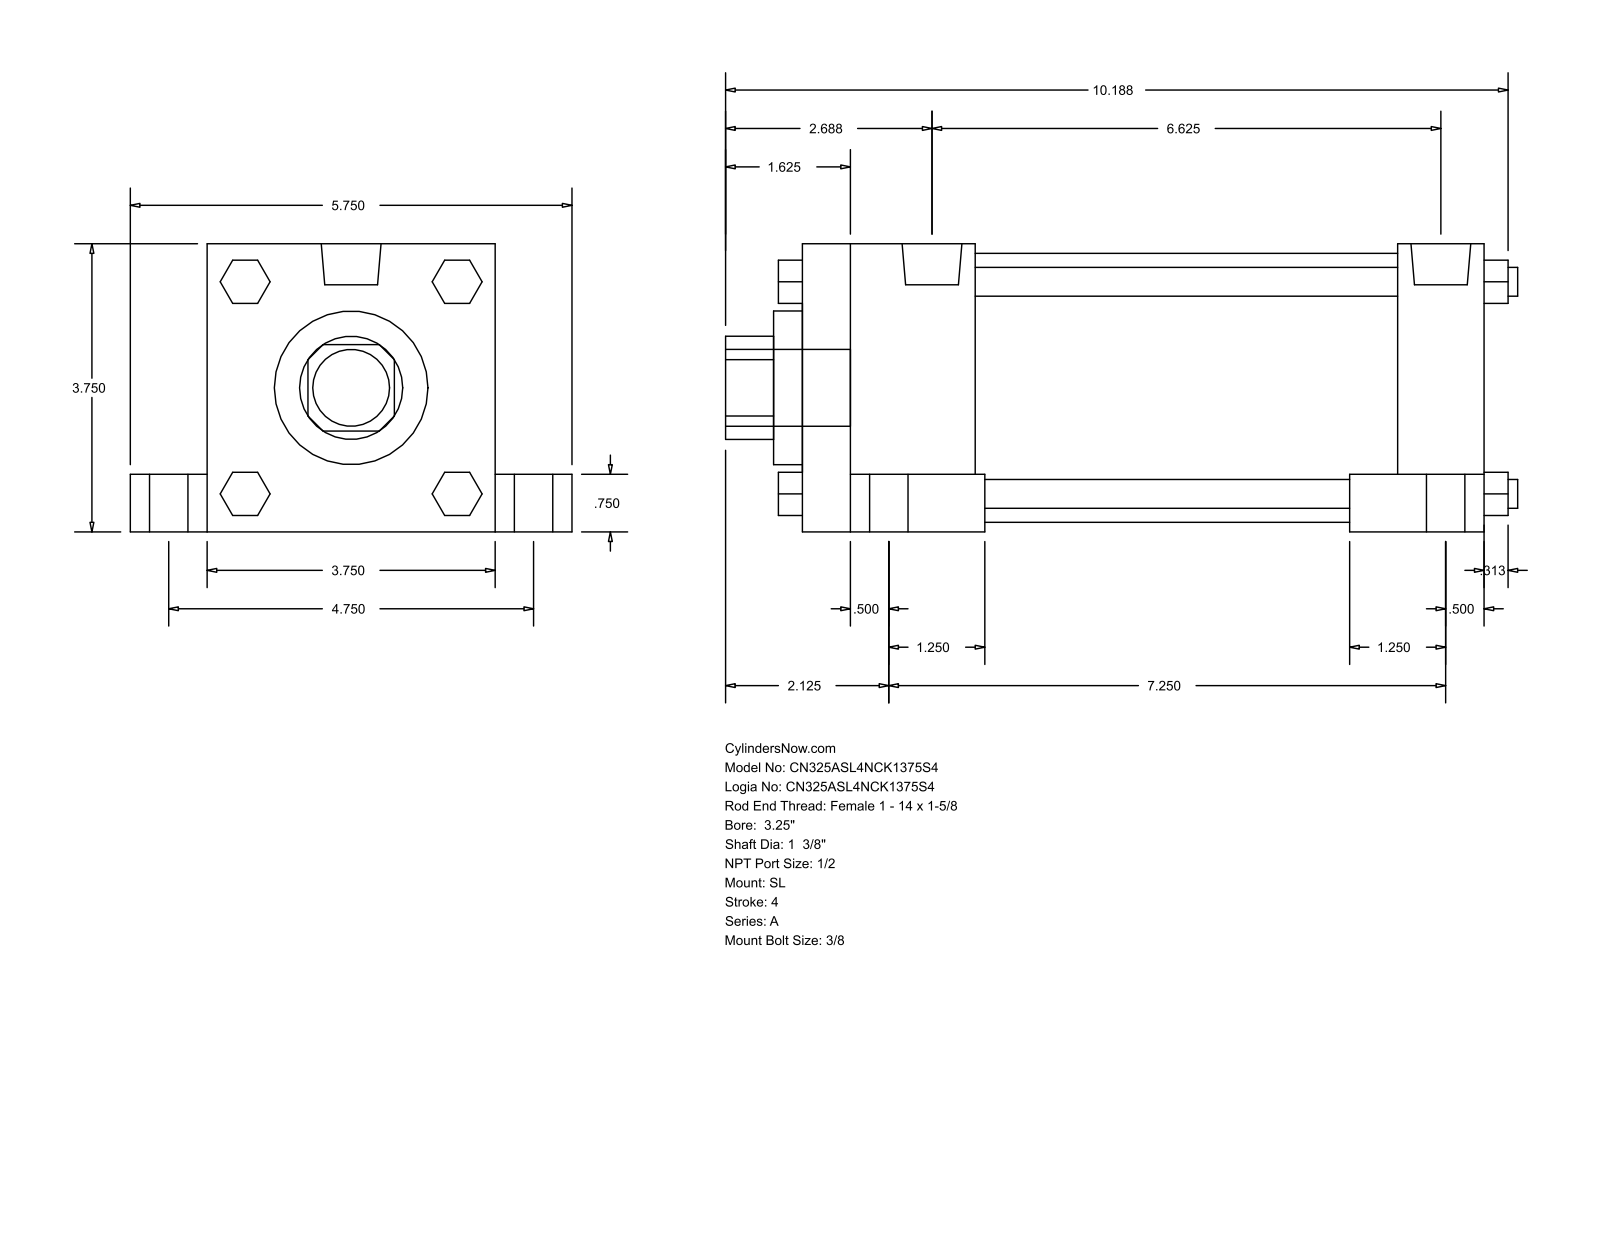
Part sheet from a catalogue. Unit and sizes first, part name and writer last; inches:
Units: inches
Overall size (bounding box): 10.313 × 5.75 × 3.75
Round holes (diameter × count): ⌀1.375 ×1, ⌀2 ×1, ⌀3.5 ×1
Round bosses / shafts (diameter × count): ⌀0.75 ×4, ⌀0.5 ×4, ⌀0.375 ×4, ⌀0.344 ×4, ⌀0.778 ×2, ⌀1 ×1
Partial cylindrical surfaces — rounded edges, fillets, slot ends (radius × count): R0.672 ×1
Main face-to-face distances: 3.75, 8.875, 1, 4.75, 0.75, 3, 0.625, 1.125, 2.25, 7.75
Bodies: 0 solids, 150 faces (114 planar, 36 cylindrical, 0 other)
Part name (STEP PRODUCT): A_SL__0325_1.375
STEP written by: GSSL Pune (CONFIG_CONTROL_DESIGN)
